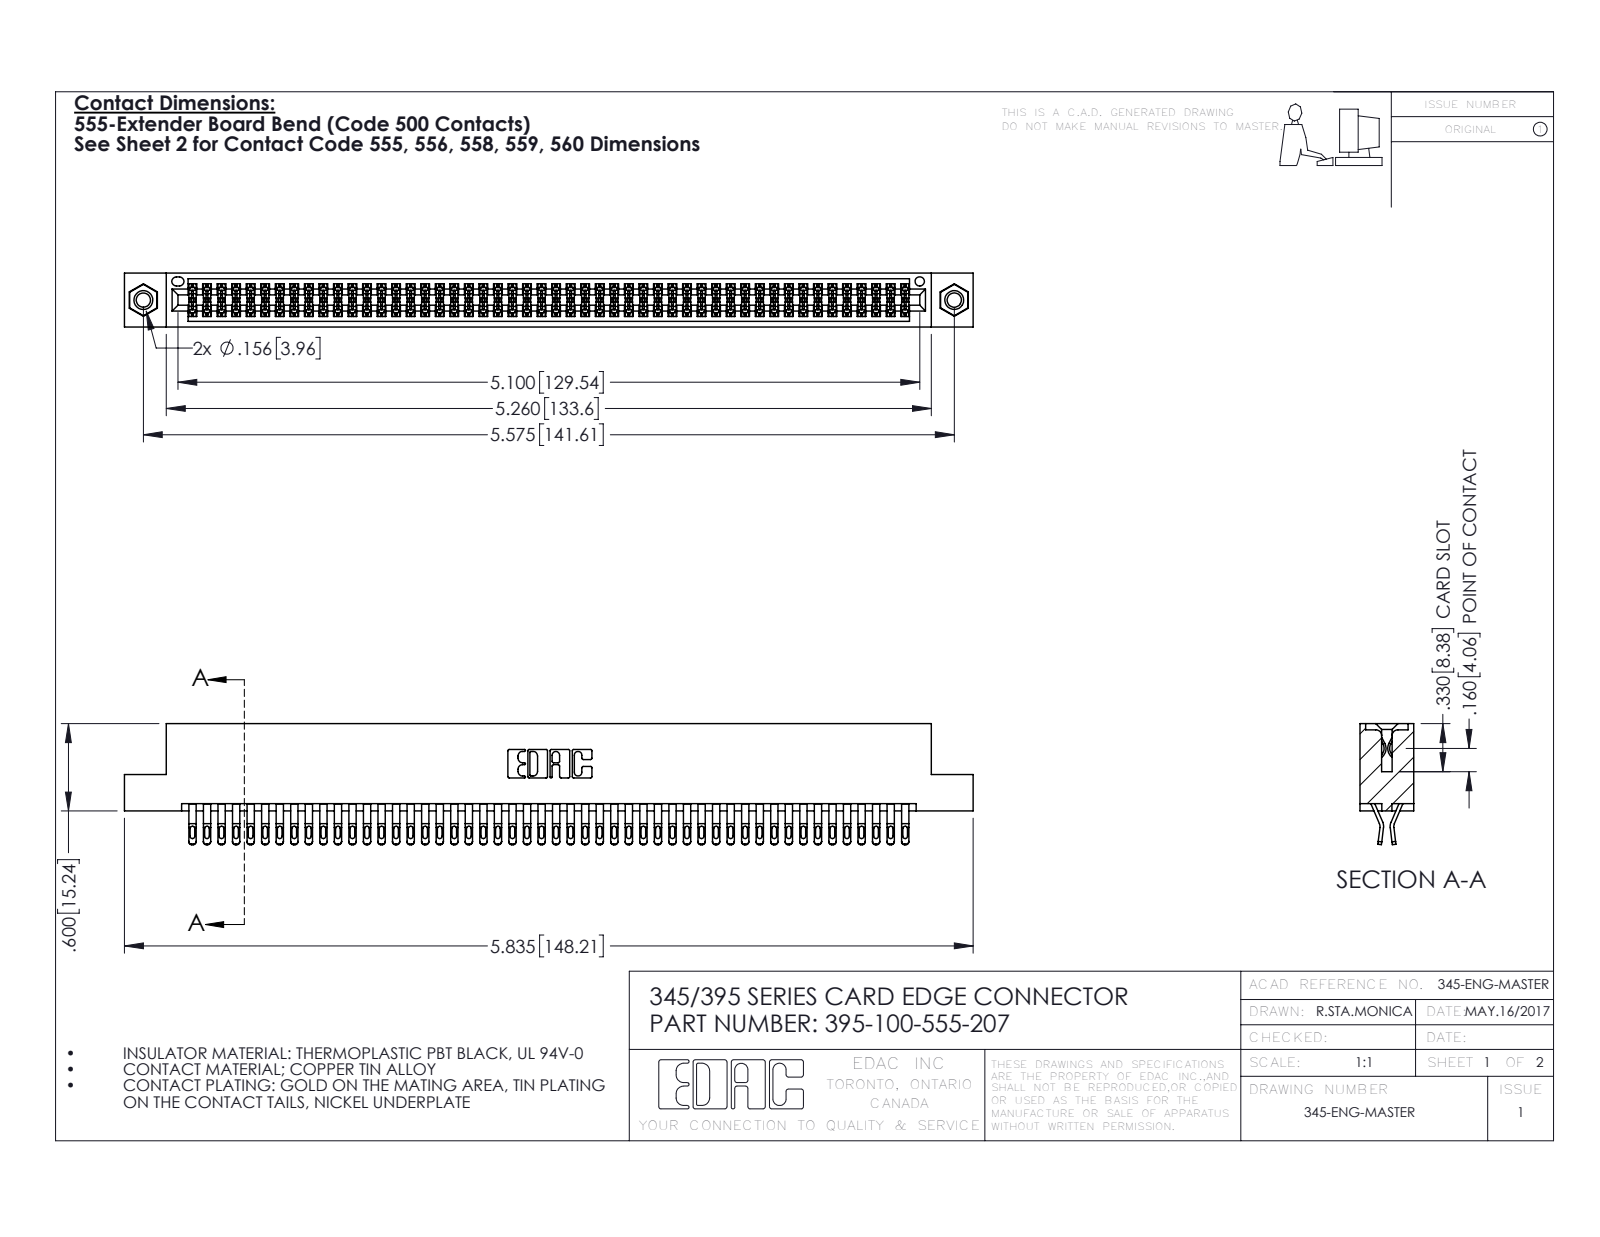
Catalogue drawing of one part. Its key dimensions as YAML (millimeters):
part_name: "395-100-555-207; 345 Part_Flush Mounting Lugs - 0.156 Dia-TI; 345-292-001_555 Tail; 345-250-001_345-250-005-103"
step_written_by: "SolidWorks 2016 (CONFIG_CONTROL_DESIGN)"
units: millimeters
bodies: {solids: 103, faces: 5786, planar: 3212, cylindrical: 2558, other: 16}
overall_size: [148.2, 21.1, 9.4]
volume: 14700
surface_area: 22990
round_holes:
  - {diameter: 2.5, count: 2}
  - {diameter: 3.2, count: 2}
  - {diameter: 4, count: 2}
  - {diameter: 1.6, count: 1}
round_bosses_or_shafts:
  - {diameter: 3.9, count: 2}
partial_cylinders:
  - {radius: 0.4, count: 250}
  - {radius: 0.5, count: 200}
  - {radius: 0.2, count: 150}
  - {radius: 0.3, count: 22}
  - {radius: 0.2, count: 6}
  - {radius: 0.8, count: 6}
  - {radius: 0.7, count: 3}
  - {radius: 0.3, count: 2}
face_to_face_distances: [1.8, 7.6, 0.6, 9.4, 5.1, 2.5, 6.9, 5.7, 4.4, 3.8]
hole_center_spacings: [6.9, 135.6, 141.6]
